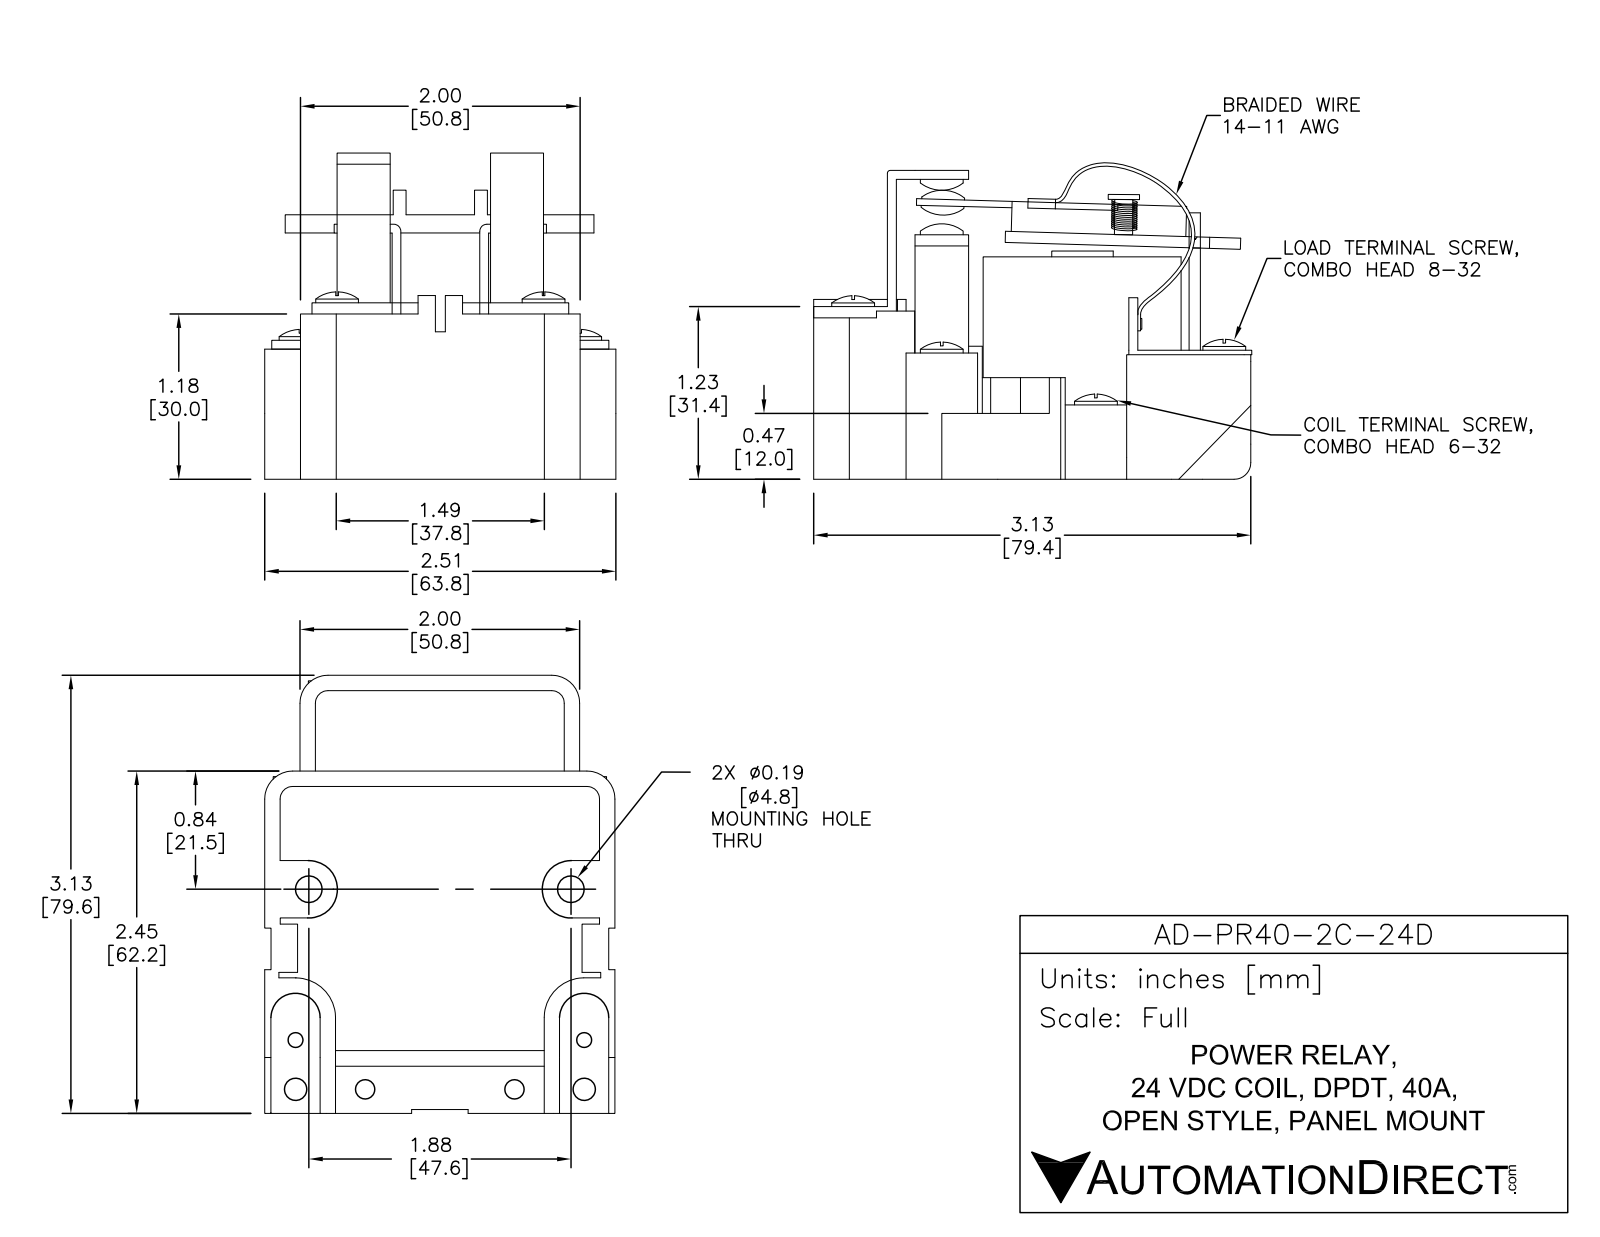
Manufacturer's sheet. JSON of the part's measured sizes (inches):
{"part_name": "AD-PR40-2C-24D", "step_written_by": "SolidWorks 2013 (AUTOMOTIVE_DESIGN)", "units": "inches", "bodies": {"solids": 37, "faces": 866, "planar": 573, "cylindrical": 185, "other": 108}, "overall_size": [3.28, 2.557, 2.167], "volume_in3": 7.775, "surface_area_in2": 66.63, "round_holes": [[0.197, 4], [0.131, 2], [0.394, 2], [1.181, 1]], "round_bosses_or_shafts": [[0.305, 6], [0.256, 6], [0.208, 4], [0.27, 2], [0.217, 2], [0.138, 2], [1.398, 1], [0.709, 1]], "partial_cylinders_radius": [[0.039, 15], [0.03, 10], [0.118, 5], [0.197, 5], [0.015, 4], [0.058, 4], [0.059, 4], [0.276, 4]], "face_to_face_distances": [0.079, 0.059, 0.039, 0.394, 0.256, 0.177, 1.427, 0.472, 1.9, 0.138], "hole_center_spacings": [0.394, 1.031, 1.083, 1.178, 1.439, 1.477, 1.939, 1.978]}
